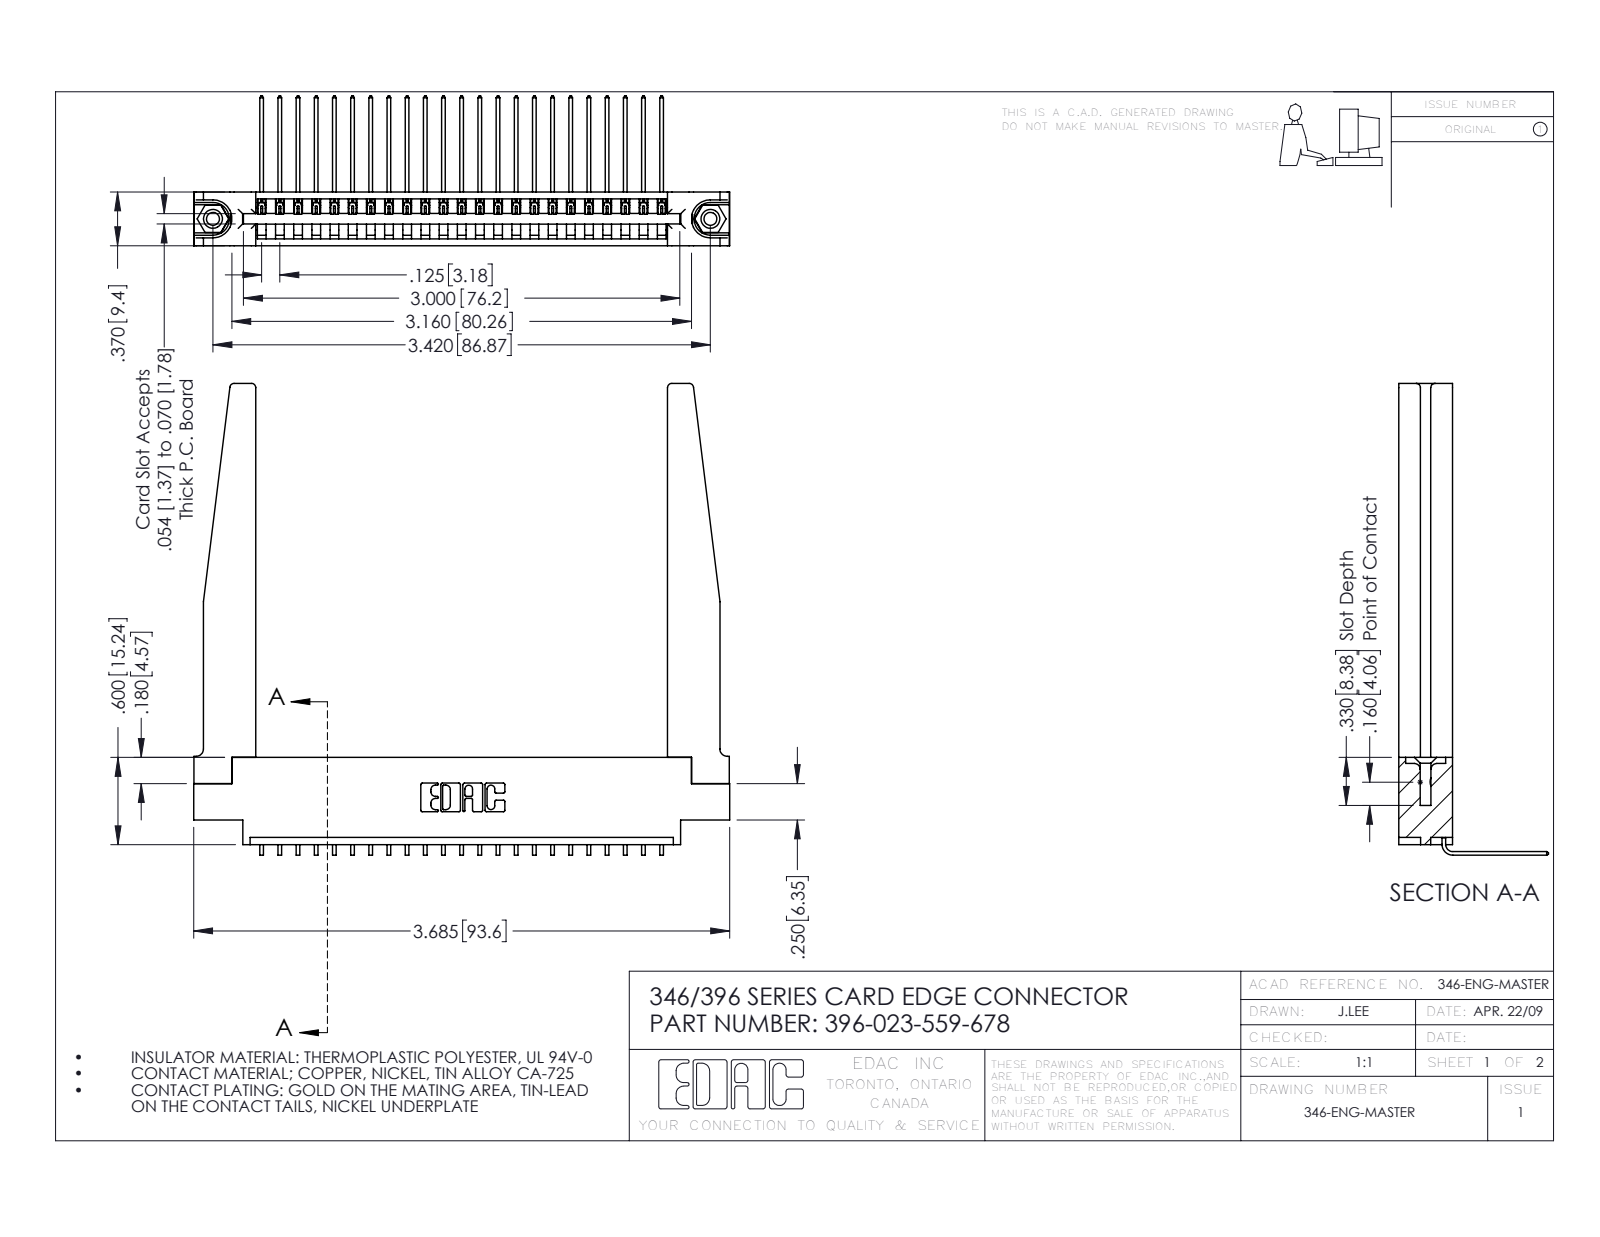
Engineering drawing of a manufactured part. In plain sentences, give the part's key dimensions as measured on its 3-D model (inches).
The part is named "345-292-001_558 559 Tail - 1; 345-250-001_345-250-001-102; 346 Part_0.170 Offset - 0.156 Dia-TH; 396-023-559-678 (+1 more)". Its 3-D file was written by "SolidWorks 2016 (CONFIG_CONTROL_DESIGN)". It is 28 solids with 1740 faces: 1188 planar, 500 cylindrical and 52 other. Overall it measures 3.685 by 3.243 by 1.03 inches. Its volume is 0.956 cubic inches and its surface area 27.73 square inches. Round holes: 2 of diameter 0.089, 2 of diameter 0.125, 2 of diameter 0.156, 1 of diameter 0.064. Round bosses or shafts: 2 of diameter 0.155. Partial cylindrical surfaces (rounded edges, fillets, slot ends): 46 of radius 0.006, 22 of radius 0.01, 8 of radius 0.03, 6 of radius 0.007, 6 of radius 0.031, 3 of radius 0.026, 3 of radius 0.05, 2 of radius 0.031. The main face-to-face distances are 0.37, 0.048, 0.072, 0.322, 0.148, 0.15, 0.025, 0.25, 0.298, 0.222. The hole center spacings are 0.246, 3.212, 3.42.
